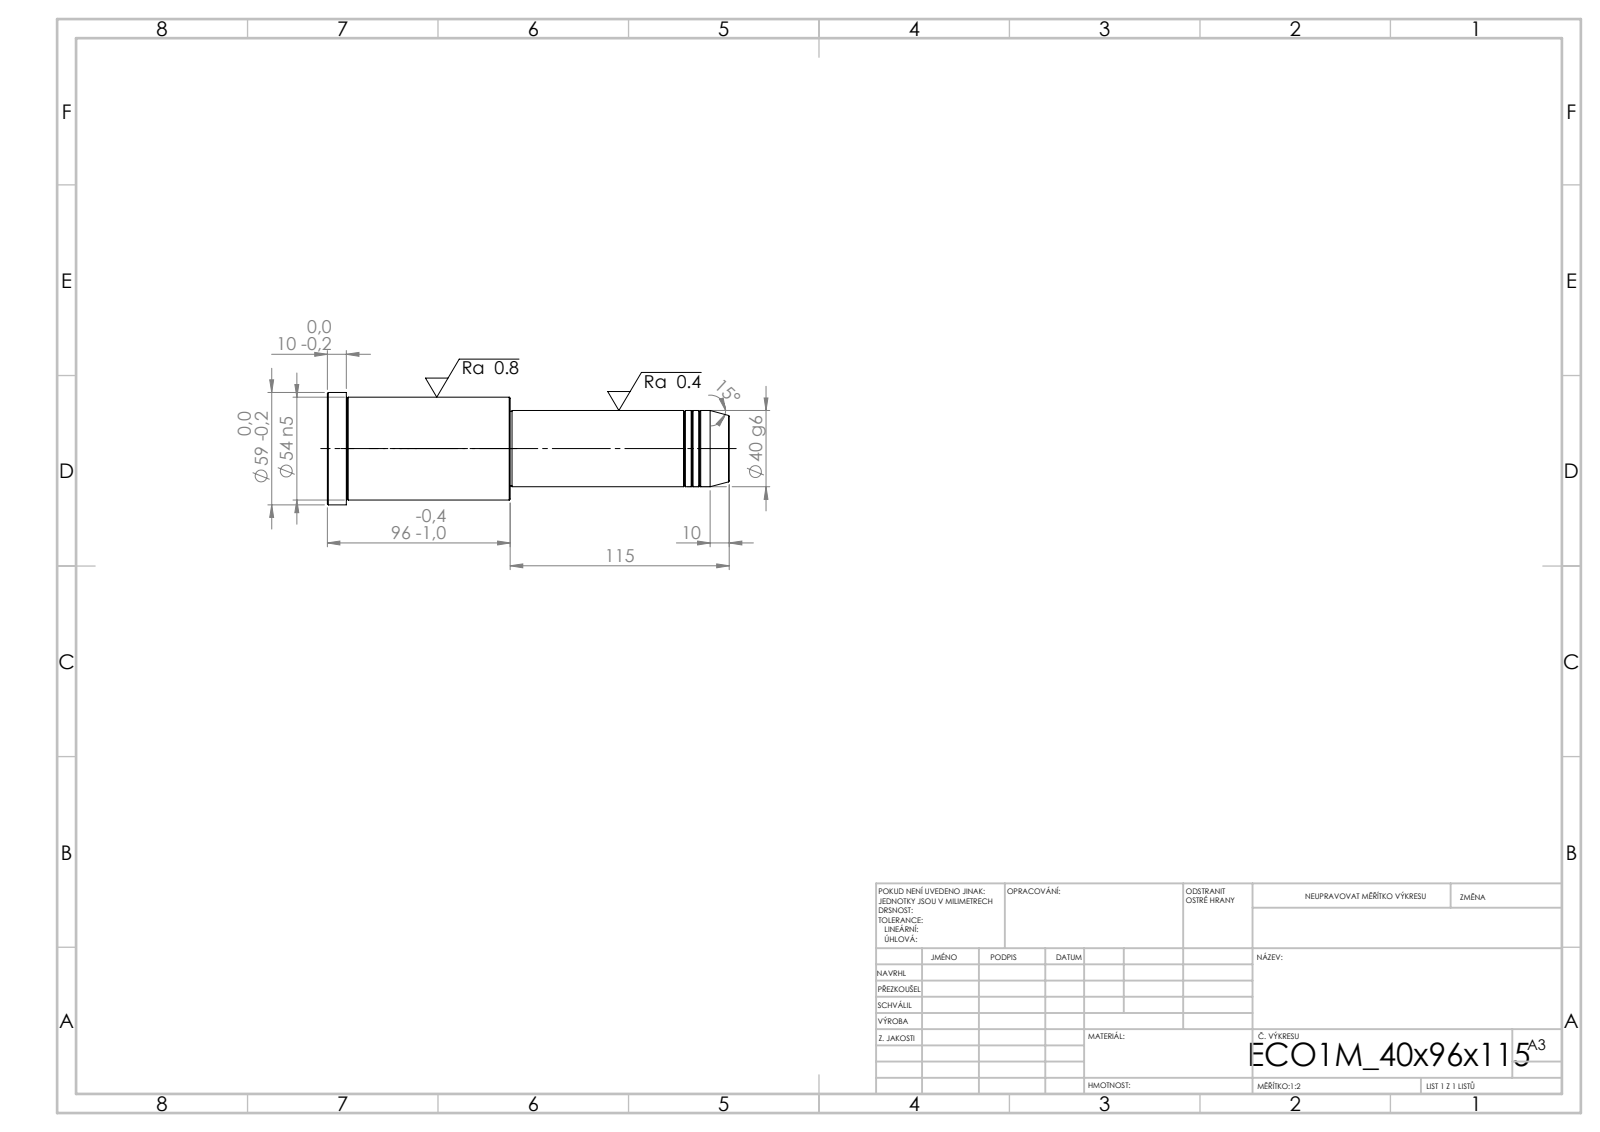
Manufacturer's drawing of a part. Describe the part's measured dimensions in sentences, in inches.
Its 3-D file was written by "SolidWorks 2019 (CONFIG_CONTROL_DESIGN)". It is 1 solid with 43 faces: 5 planar, 14 cylindrical and 24 other. Overall it measures 8.307 by 2.323 by 2.323 inches. Its volume is 22.39 cubic inches and its surface area 56.28 square inches. Round bosses or shafts: 1 of diameter 2.323, 1 of diameter 2.126, 1 of diameter 1.575, 1 of diameter 1.535. The main face-to-face distances are 3.78, 4.528, 8.307, 7.913, 3.386, 0.394, 4.488, 0.039, 3.425, 3.819.
